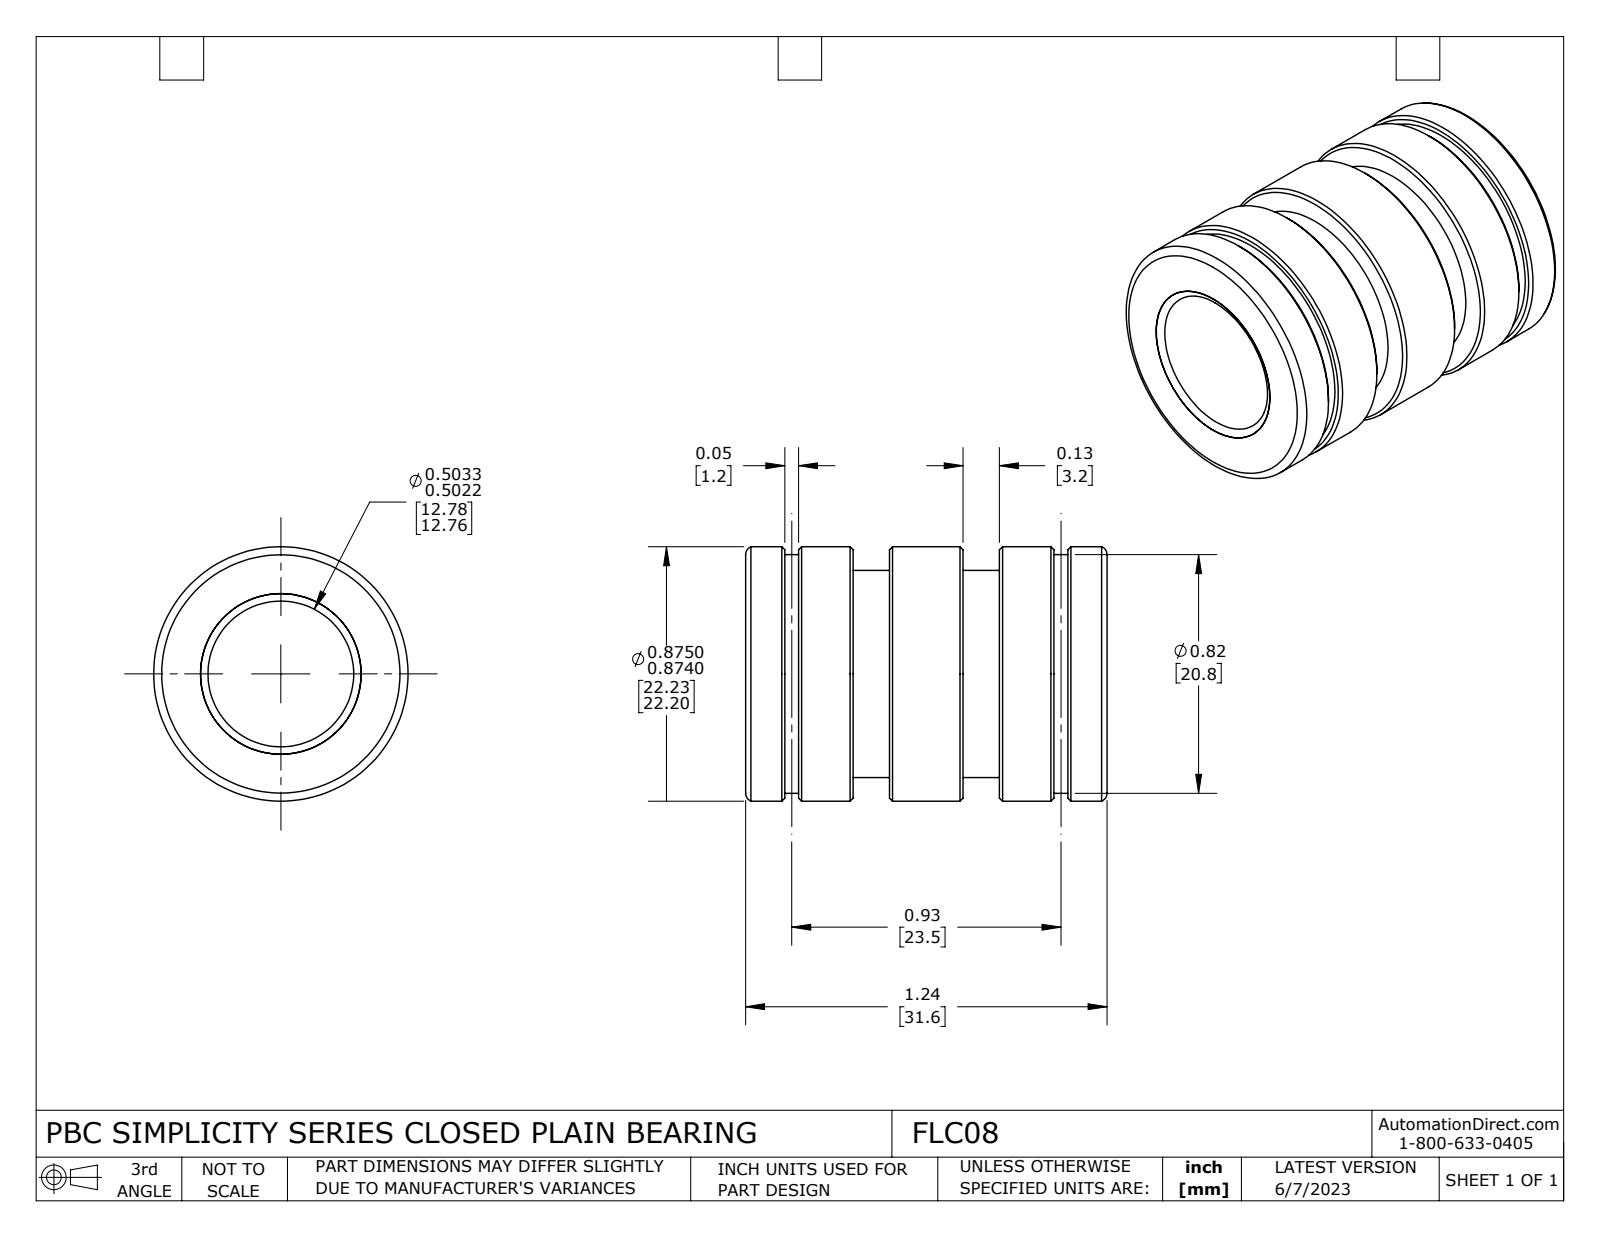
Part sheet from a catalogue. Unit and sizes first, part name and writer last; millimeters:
Units: millimetres
Overall size (bounding box): 31.6 × 22.2 × 22.2
Round holes (diameter × count): ⌀12.7 ×1, ⌀14 ×1
Round bosses / shafts (diameter × count): ⌀22.2 ×1, ⌀20.8 ×1, ⌀18.1 ×1
Main face-to-face distances: 9.4, 12.6, 19, 22.2, 3.2, 9.6, 31.6, 12.8, 6.4, 3.4
Volume: 7 230 mm³ · Surface area: 7 232 mm²
Bodies: 2 solids, 58 faces (10 planar, 24 cylindrical, 24 other)
Part name (STEP PRODUCT): FLC08
STEP written by: SolidWorks 2021 (CONFIG_CONTROL_DESIGN)
